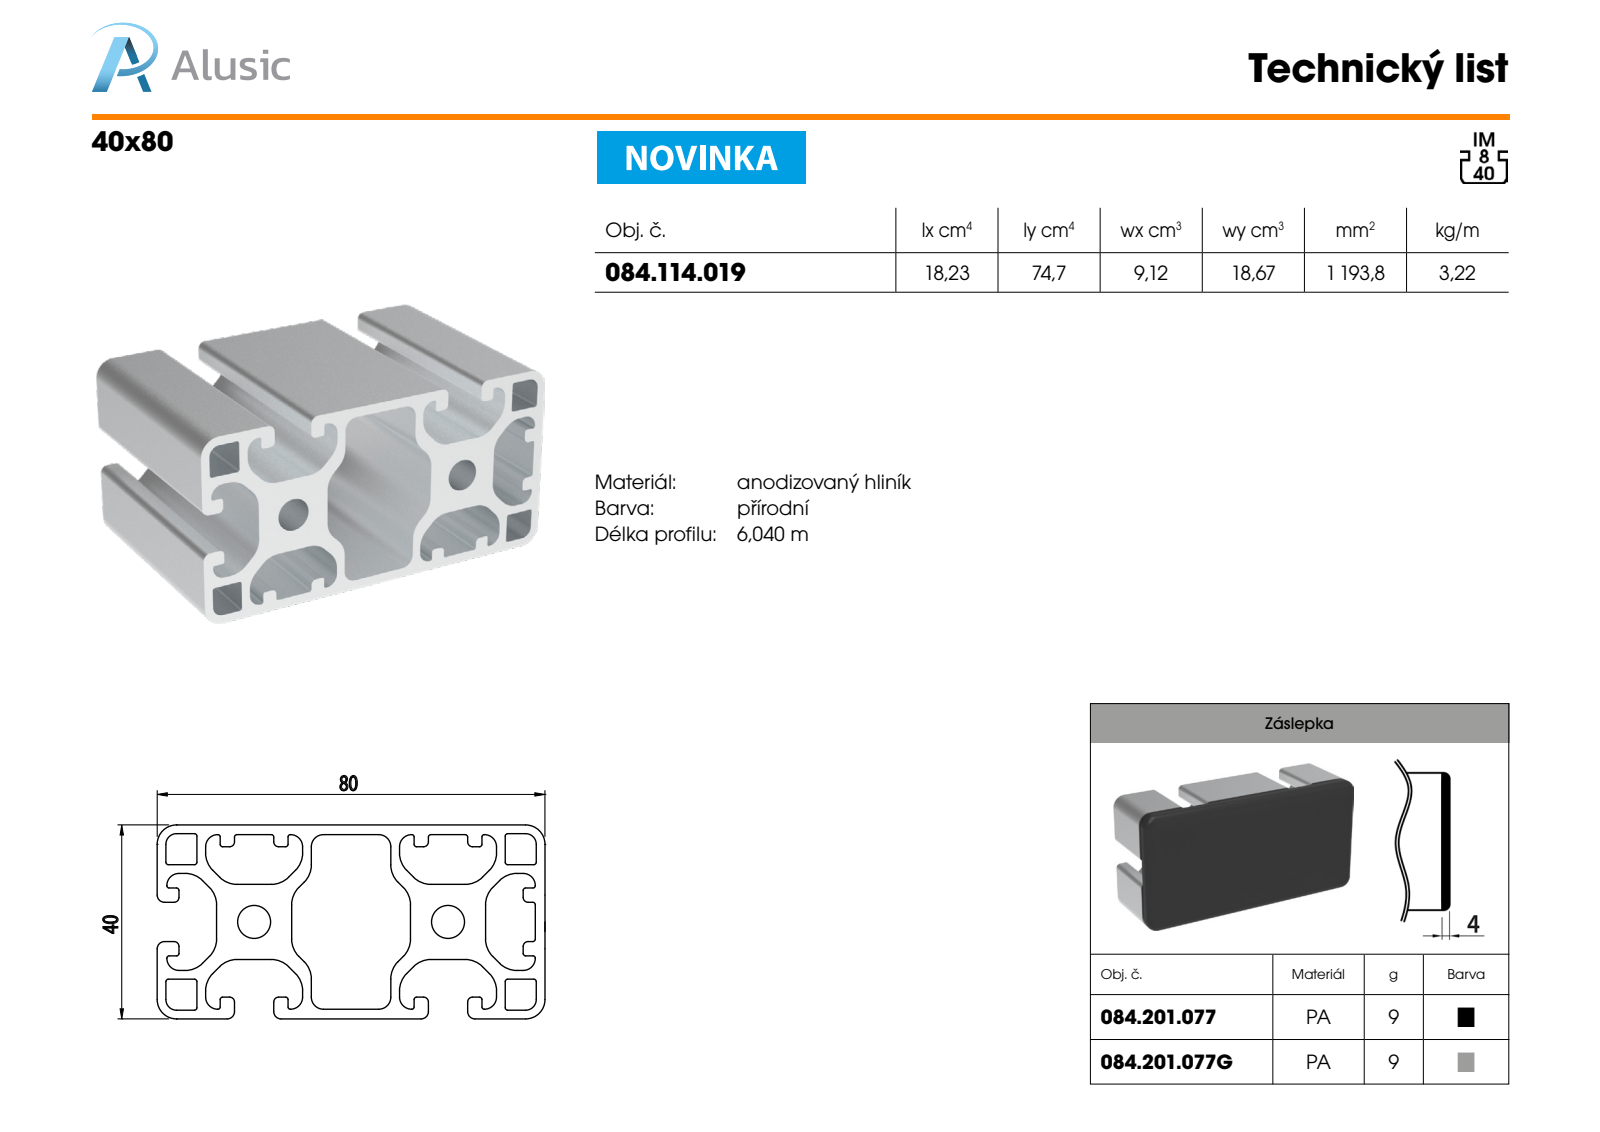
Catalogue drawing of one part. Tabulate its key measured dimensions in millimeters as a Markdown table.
| quantity | value |
| --- | --- |
| part name | 084.114.019 |
| STEP written by | SolidWorks 2018 (AUTOMOTIVE_DESIGN) |
| units | millimeters |
| bodies | 1 solid, 238 faces (117 planar, 121 cylindrical, 0 other) |
| overall size | 100 × 80 × 40 |
| volume | 119 385 mm³ |
| surface area | 82 372 mm² |
| round holes (diameter × count) | 6.8 × 2 |
| partial cylindrical surfaces (radius × count) | 5 × 32, 0.5 × 30, 2.5 × 16, 0.45 × 12, 1 × 12, 1.5 × 6, 2.2 × 4, 4 × 4 |
| main face-to-face distances | 40, 19.55, 4.05, 8.2, 2, 27.75, 12.25, 38, 31.8, 30 |
| hole center spacings | 40 |
